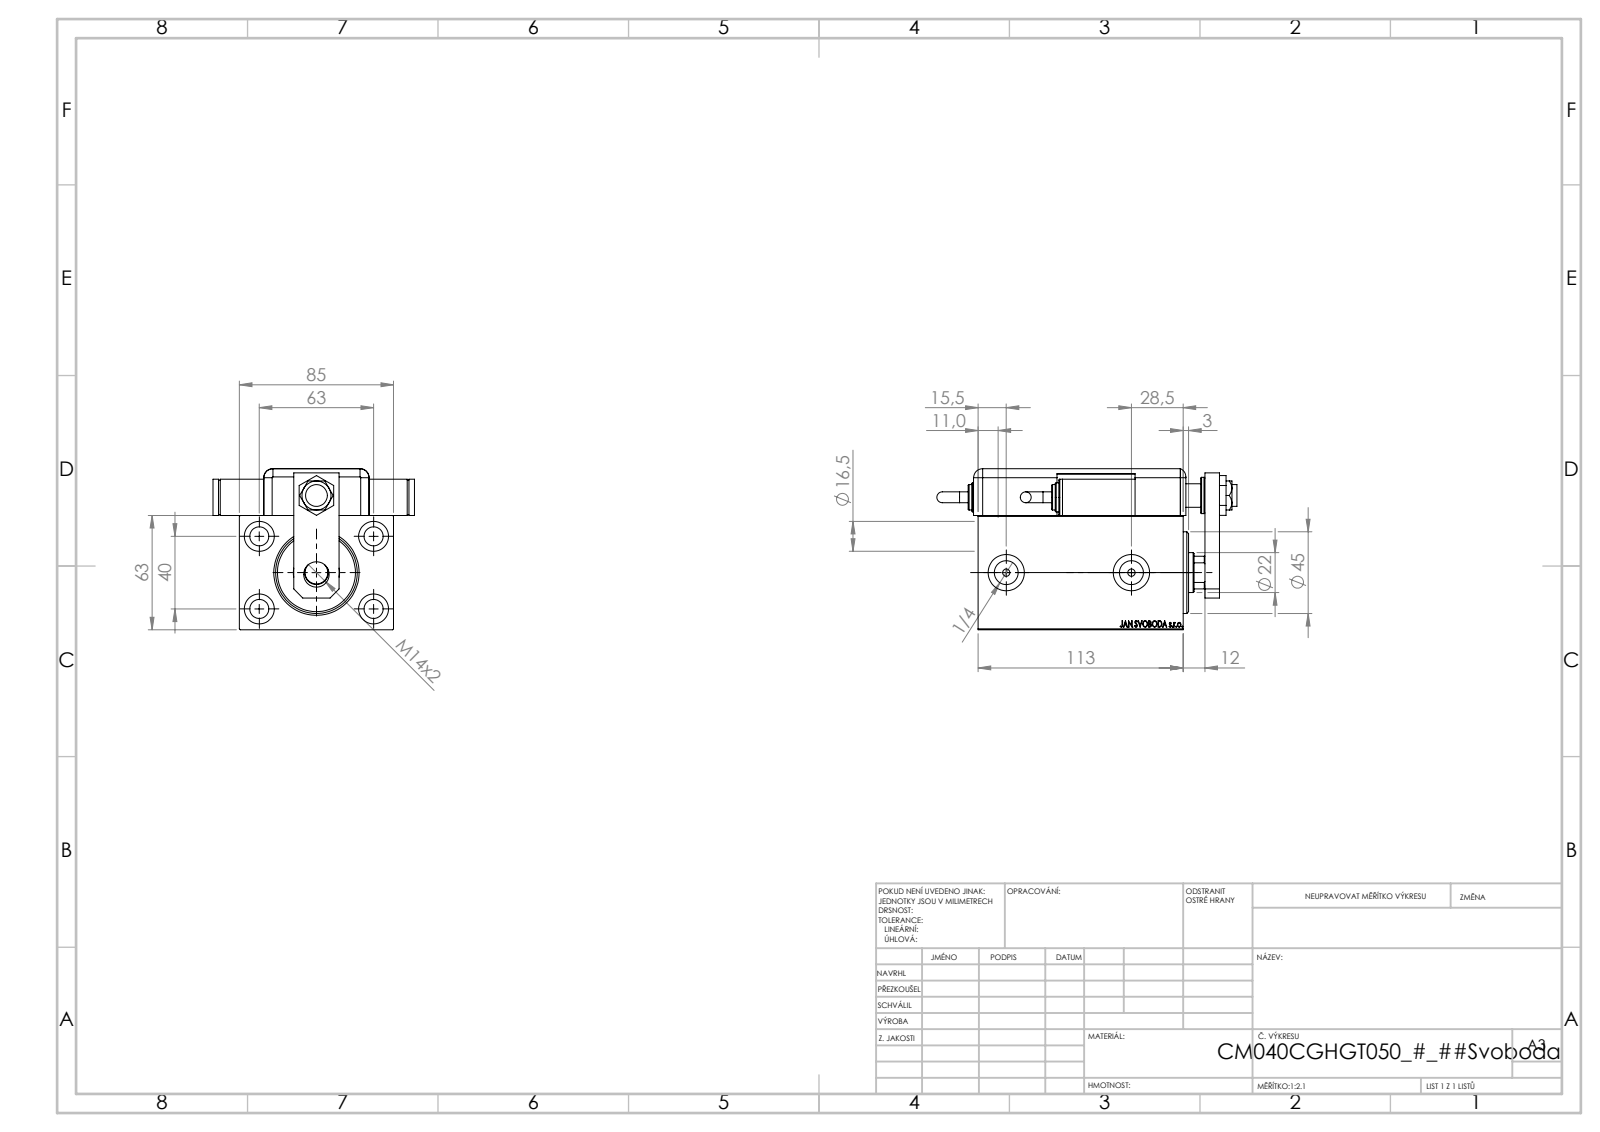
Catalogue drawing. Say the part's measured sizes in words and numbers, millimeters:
The part is named "TYC; ZARAZKA_Q; V450CM_VC_B; NUT_D13 (+7 more)". Its 3-D file was written by "SolidWorks 2019 (CONFIG_CONTROL_DESIGN)". It is 13 solids with 1246 faces: 614 planar, 115 cylindrical and 517 other. Overall it measures 165.46 by 111 by 88.8 millimeters. Its volume is 657 266 cubic millimeters and its surface area 149 535 square millimeters. Round holes: 4 of diameter 4, 4 of diameter 10.5, 4 of diameter 16.5, 2 of diameter 8, 2 of diameter 13.16, 2 of diameter 14, 2 of diameter 20, 1 of diameter 12, 1 of diameter 12.5, 1 of diameter 13, 1 of diameter 22, 1 of diameter 25.5. Round bosses or shafts: 3 of diameter 20, 2 of diameter 16, 2 of diameter 14, 2 of diameter 6. Partial cylindrical surfaces (rounded edges, fillets, slot ends): 9 of radius 5, 1 of radius 10, 1 of radius 10.5. The main face-to-face distances are 3, 63, 13.5, 85, 12, 25.8, 88.8, 20, 83, 113. The hole center spacings are 37.31, 36.79, 37.86, 38.71, 40, 63, 69.99, 74.63.
